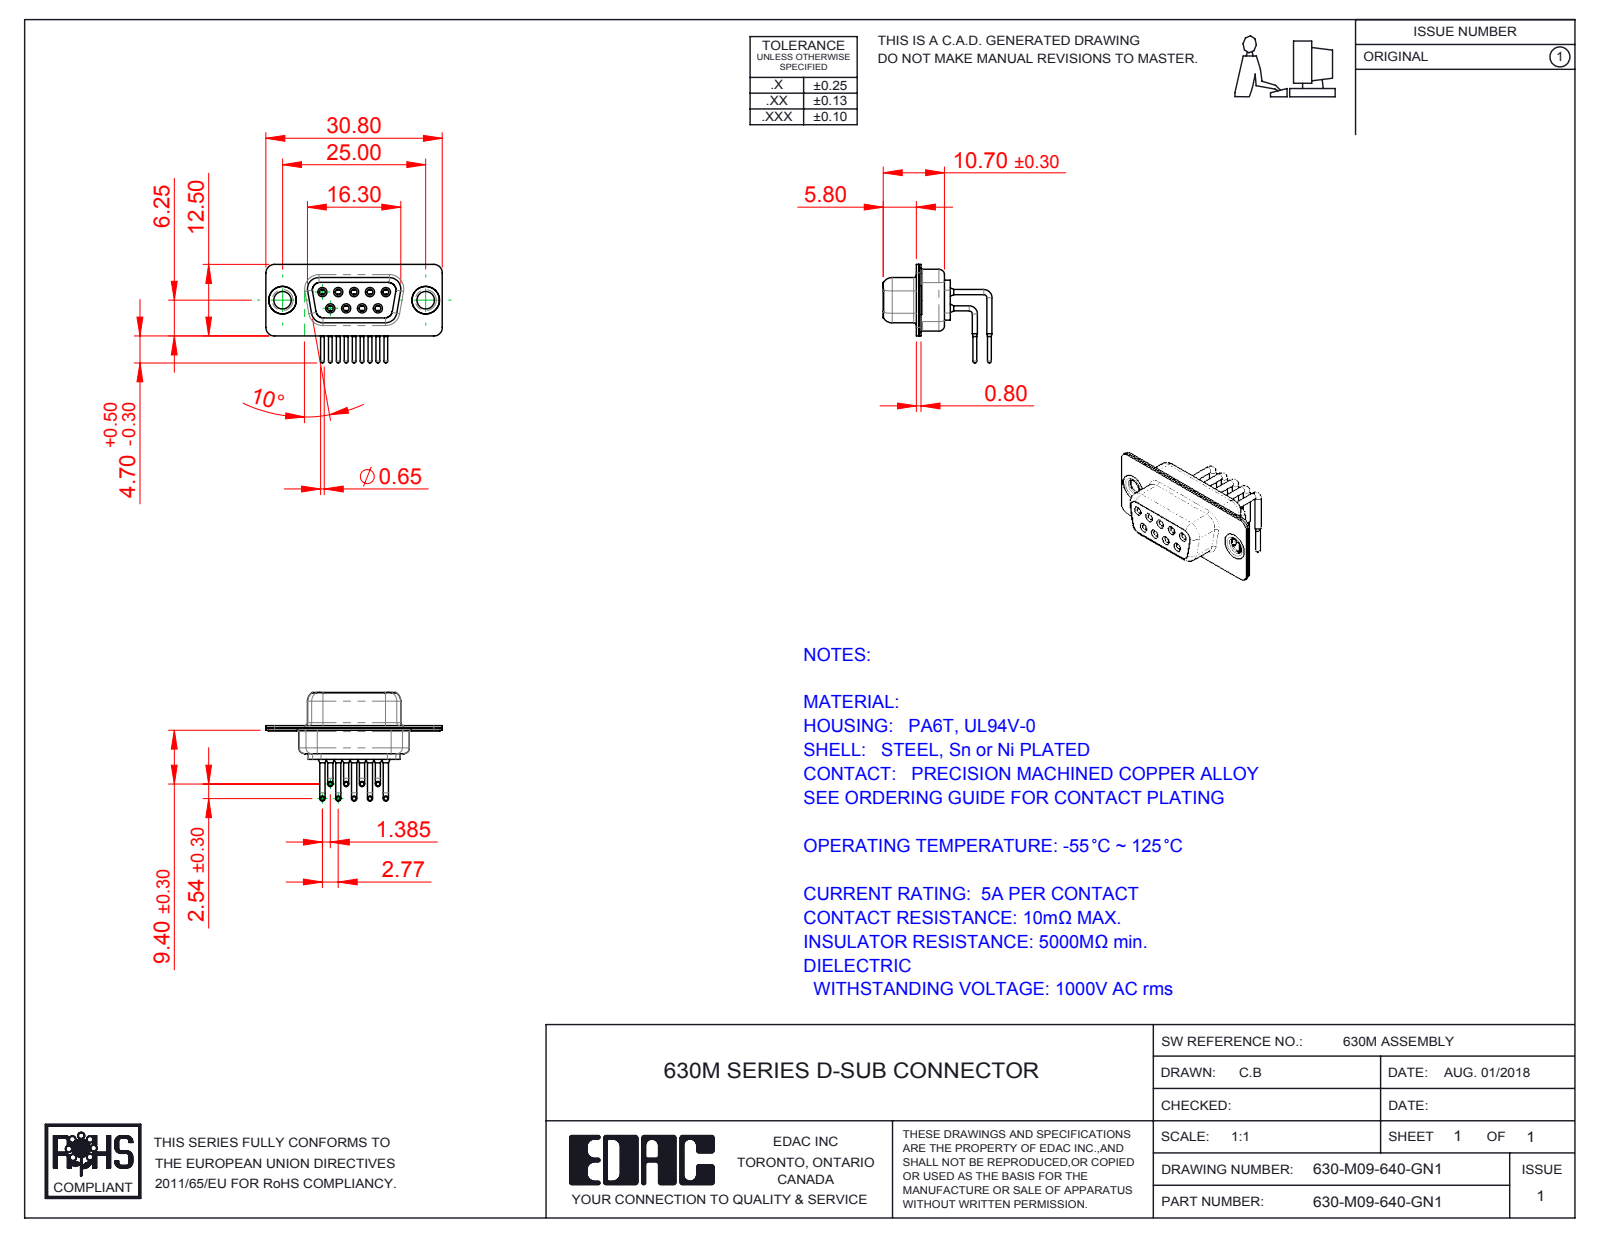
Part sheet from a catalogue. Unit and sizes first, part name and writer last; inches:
Units: inches
Overall size (bounding box): 1.213 × 0.748 × 0.677
Round holes (diameter × count): ⌀0.039 ×9, ⌀0.043 ×9, ⌀0.067 ×9, ⌀0.071 ×9, ⌀0.079 ×9, ⌀0.12 ×2, ⌀0.157 ×2, ⌀0.189 ×2
Round bosses / shafts (diameter × count): ⌀0.035 ×18, ⌀0.063 ×9, ⌀0.059 ×9, ⌀0.026 ×9, ⌀0.197 ×2, ⌀0.193 ×2, ⌀0.14 ×2
Partial cylindrical surfaces — rounded edges, fillets, slot ends (radius × count): R0.059 ×16, R0.079 ×12, R0.053 ×8, R0.063 ×8, R0.01 ×4, R0.02 ×4, R0.024 ×4, R0.026 ×4
Main face-to-face distances: 0.016, 0.031, 0.057, 0.352, 0.091, 0.244, 0.335, 0.075, 0.033, 0.368
Hole centre spacings: 0.124, 0.109, 0.218, 0.198, 0.198, 0.327, 0.28, 0.294
Volume: 0.103 in³ · Surface area: 6.96 in²
Bodies: 14 solids, 730 faces (202 planar, 328 cylindrical, 200 other)
Part name (STEP PRODUCT): 630M Thru Hole Rivet; 630-M09-640-GN1; 630M Shell Rear_09 Contacts; 630M Housing_09 Contacts (+3 more)
STEP written by: SolidWorks 2016 (CONFIG_CONTROL_DESIGN)
